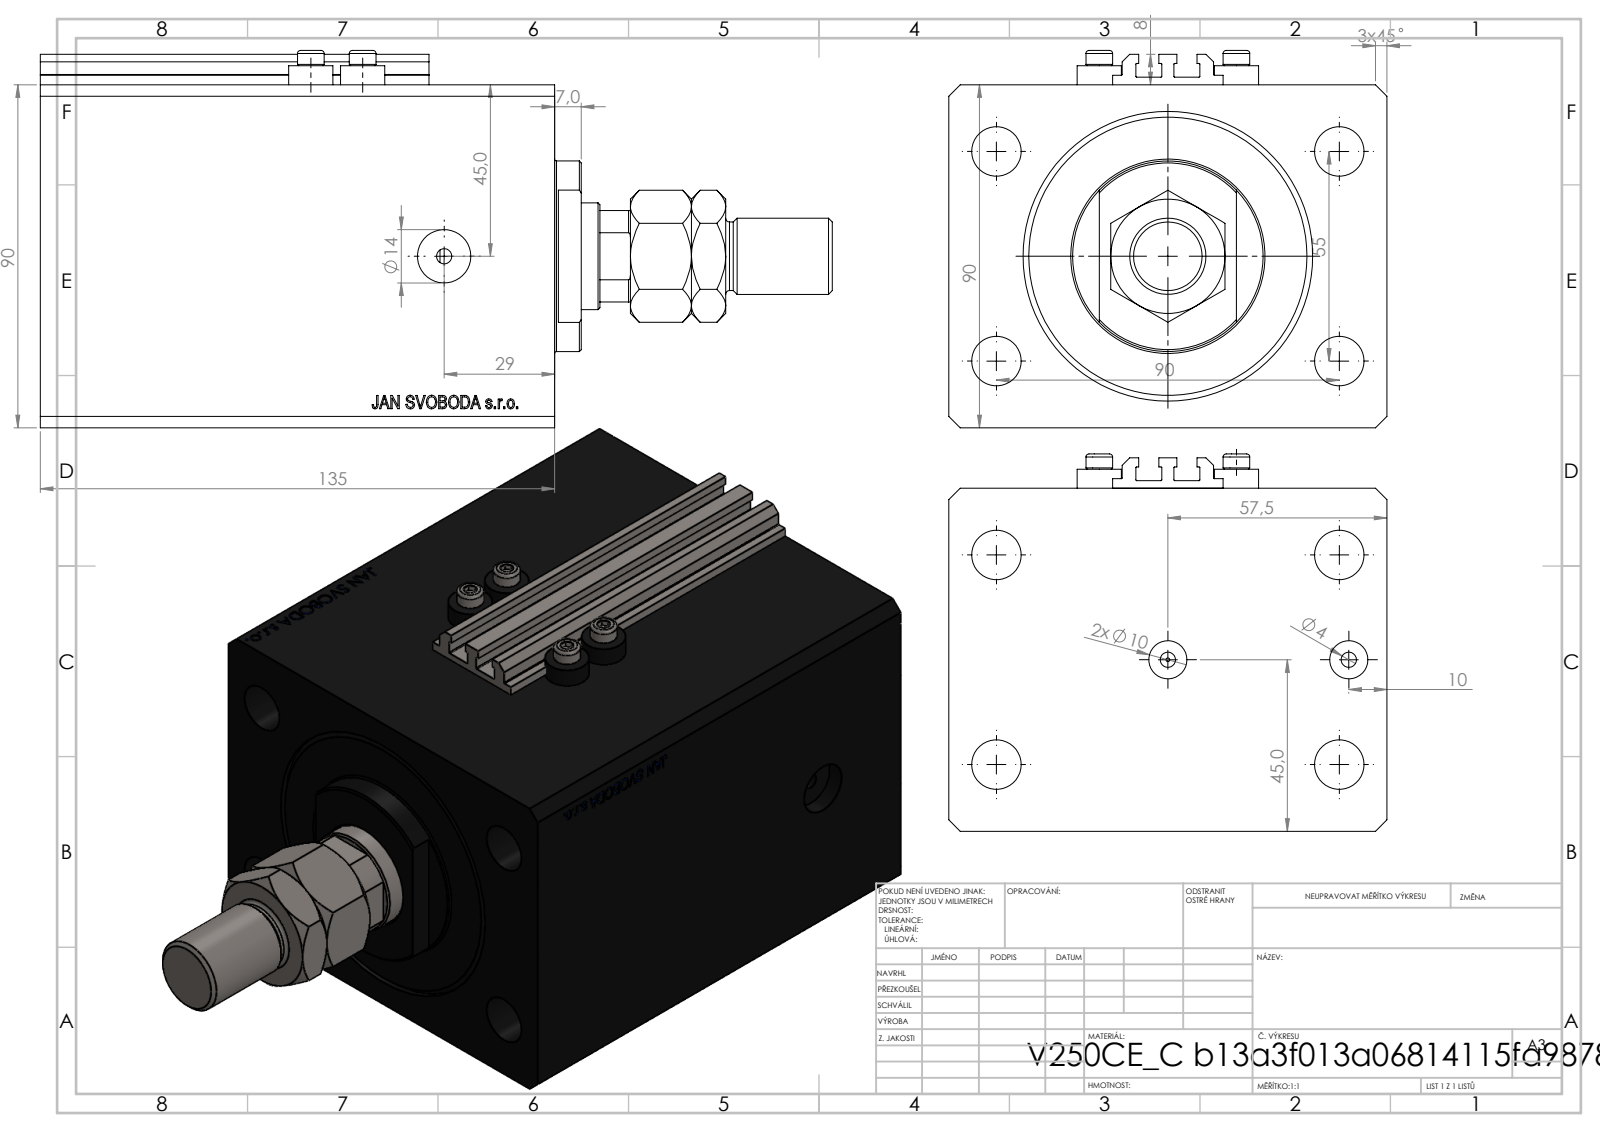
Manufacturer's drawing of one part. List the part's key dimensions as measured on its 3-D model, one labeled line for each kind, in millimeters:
Part name (STEP PRODUCT): V250CE_VC_C; V250CE_C_Body; ALLEN BOLT V250CE; MTA (+1 more)
STEP written by: SolidWorks 2019 (CONFIG_CONTROL_DESIGN)
Units: millimetres
Bodies: 9 solids, 1087 faces (519 planar, 92 cylindrical, 476 other)
Overall size (bounding box): 207.9 × 115 × 99
Volume: 1 247 000 mm³ · Surface area: 185 146 mm²
Round holes (diameter × count): ⌀4 ×8, ⌀13 ×4, ⌀10 ×2, ⌀14 ×2, ⌀1.25 ×1, ⌀18.5 ×1, ⌀28 ×1, ⌀63 ×1, ⌀76 ×1
Round bosses / shafts (diameter × count): ⌀11.6 ×4, ⌀7 ×4, ⌀50 ×1, ⌀20 ×1, ⌀18 ×1
Partial cylindrical surfaces — rounded edges, fillets, slot ends (radius × count): R0.2 ×10, R13.5 ×1
Main face-to-face distances: 90, 115, 135, 17.9, 117.1, 87, 104.9, 30.1, 50, 54.9
Hole centre spacings: 52.74, 13.6, 27.61, 36, 38.48, 55, 90, 96.5
